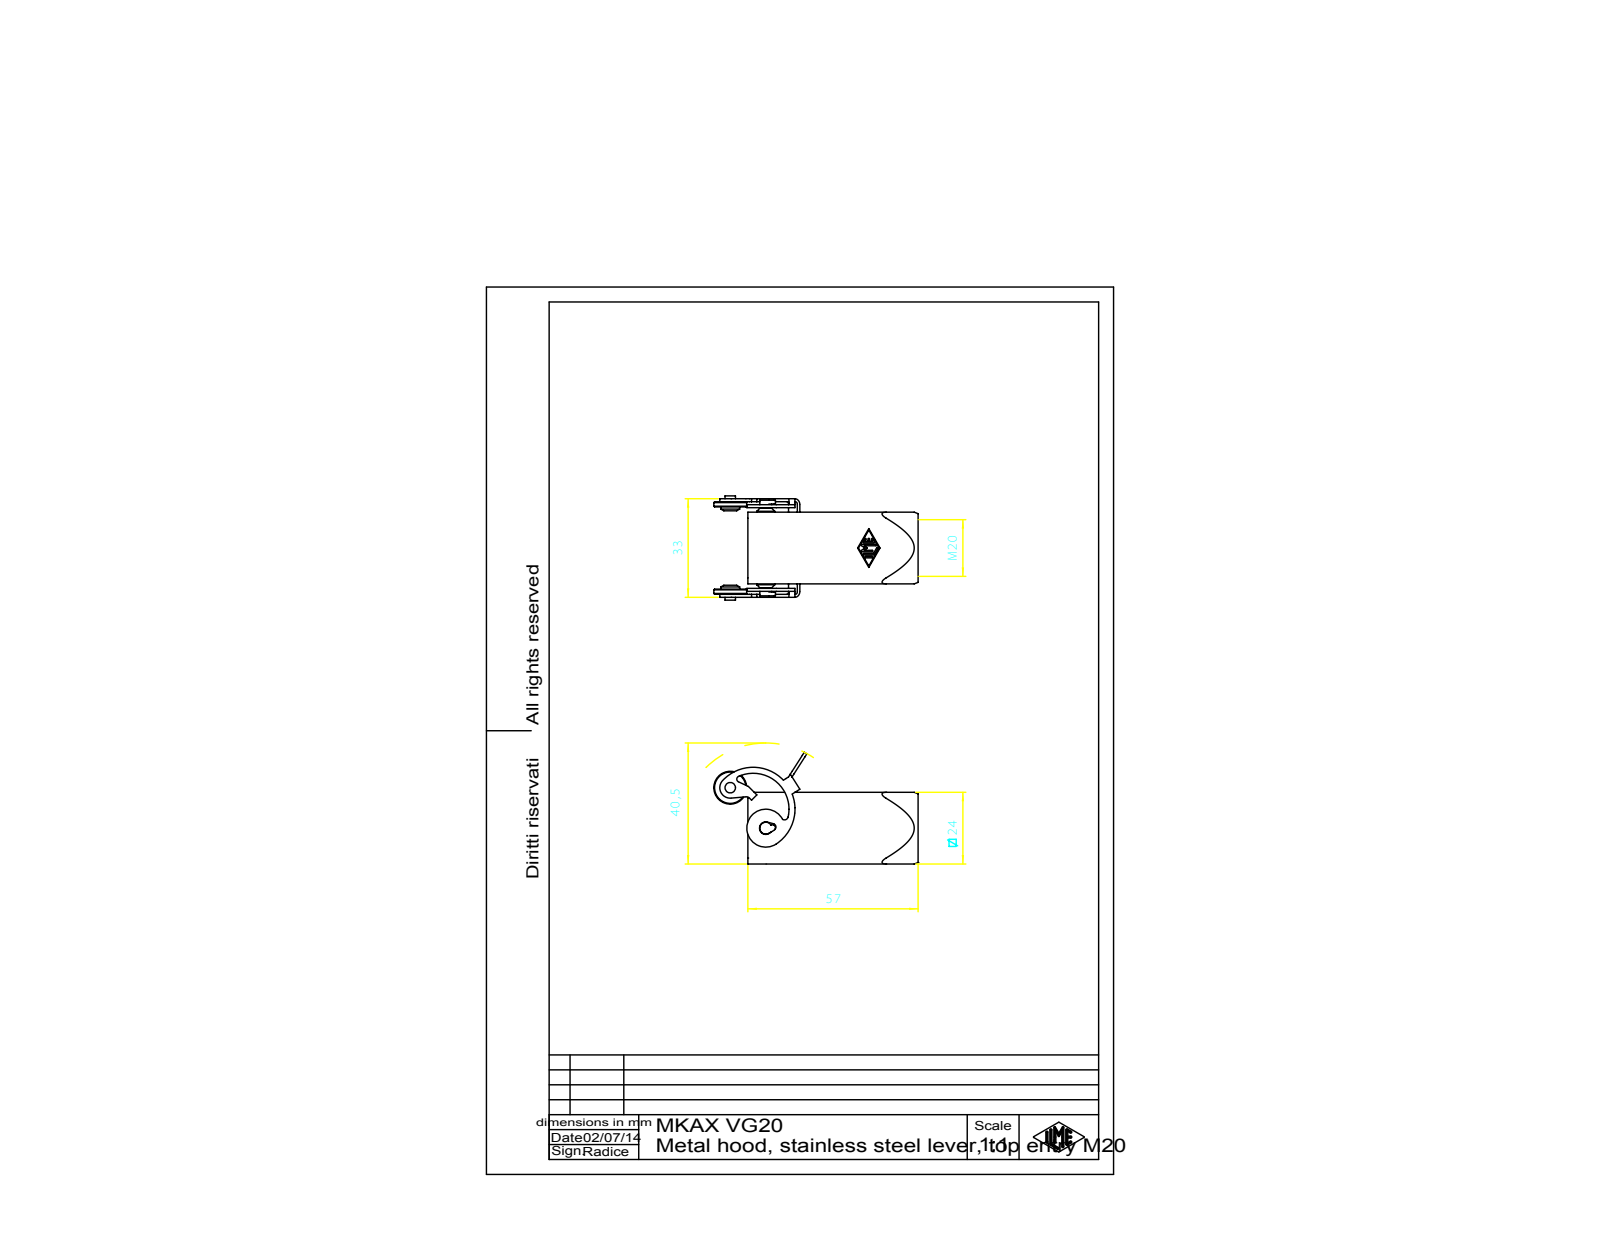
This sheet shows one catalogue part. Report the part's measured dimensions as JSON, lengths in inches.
{"part_name": "MKAX VG20", "step_written_by": "Autodesk Inventor 7 (AUTOMOTIVE_DESIGN)", "units": "inches", "bodies": {"solids": 2, "faces": 237, "planar": 81, "cylindrical": 90, "other": 66}, "overall_size": [2.476, 1.473, 1.374], "volume_in3": 0.486, "surface_area_in2": 18.91, "round_holes": [[0.13, 1], [0.591, 1], [0.787, 1]], "round_bosses_or_shafts": [[0.433, 1], [0.248, 1], [0.236, 1], [0.157, 1], [0.138, 1]], "partial_cylinders_radius": [[0.079, 18], [0.01, 14], [0.039, 6], [0.031, 2], [0.043, 1], [0.049, 1], [0.059, 1], [0.083, 1]], "face_to_face_distances": [0.039, 0.906, 0.945, 0.866, 0.079, 0.118, 0.098, 1.004, 0.138, 1.043]}
